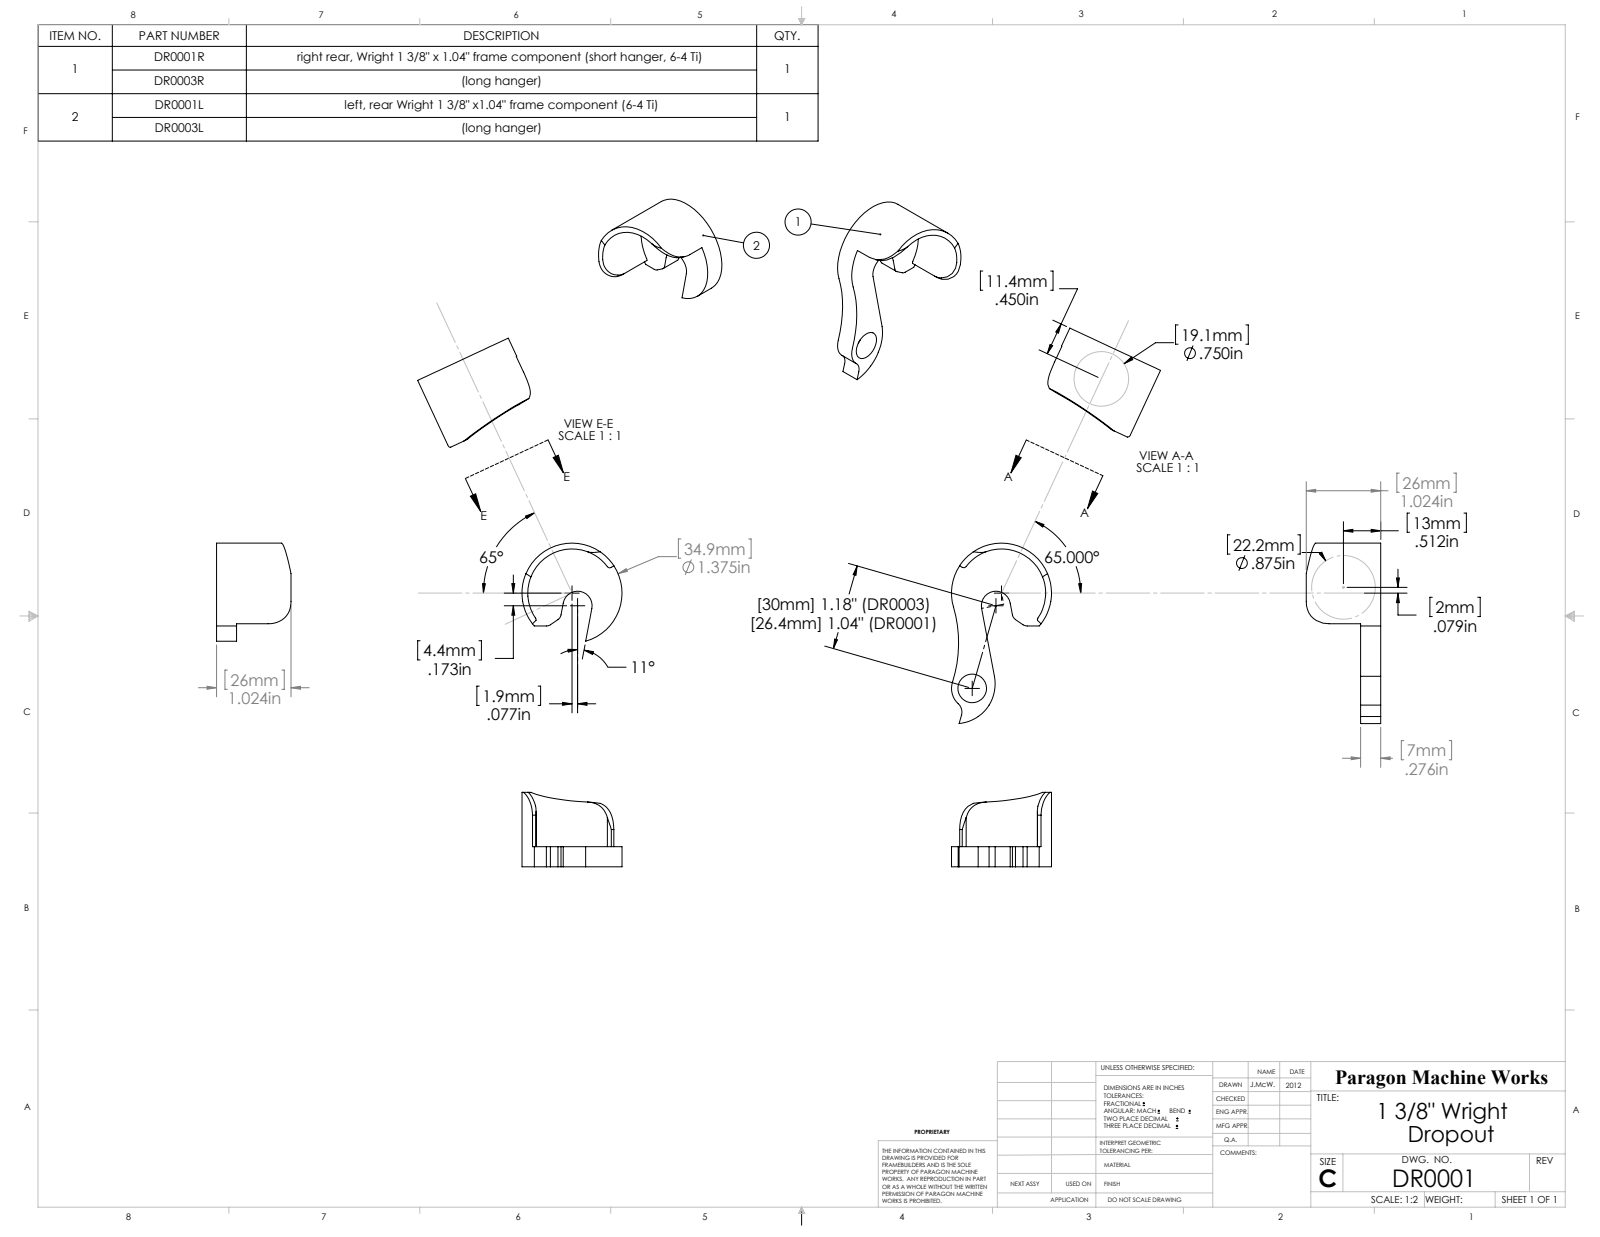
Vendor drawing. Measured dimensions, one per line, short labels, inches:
name: DR0001; DR0001L; DR0001R
written by: SolidWorks 2012 (AUTOMOTIVE_DESIGN)
unit: in
bodies: 2 solids, 53 faces (21 planar, 32 cylindrical, 0 other)
size: 7.281 × 2.48 × 1.024
volume: 0.983 in³; area: 15.04 in²
holes: 1× ⌀0.394
bosses: 1× ⌀1.375
rounds: 4× R0.04, 4× R0.1, 2× R0.2, 2× R0.315, 2× R0.378, 2× R0.607, 1× R0.156, 1× R0.285
face distances: 0.276, 0.4, 1.024, 0.748
